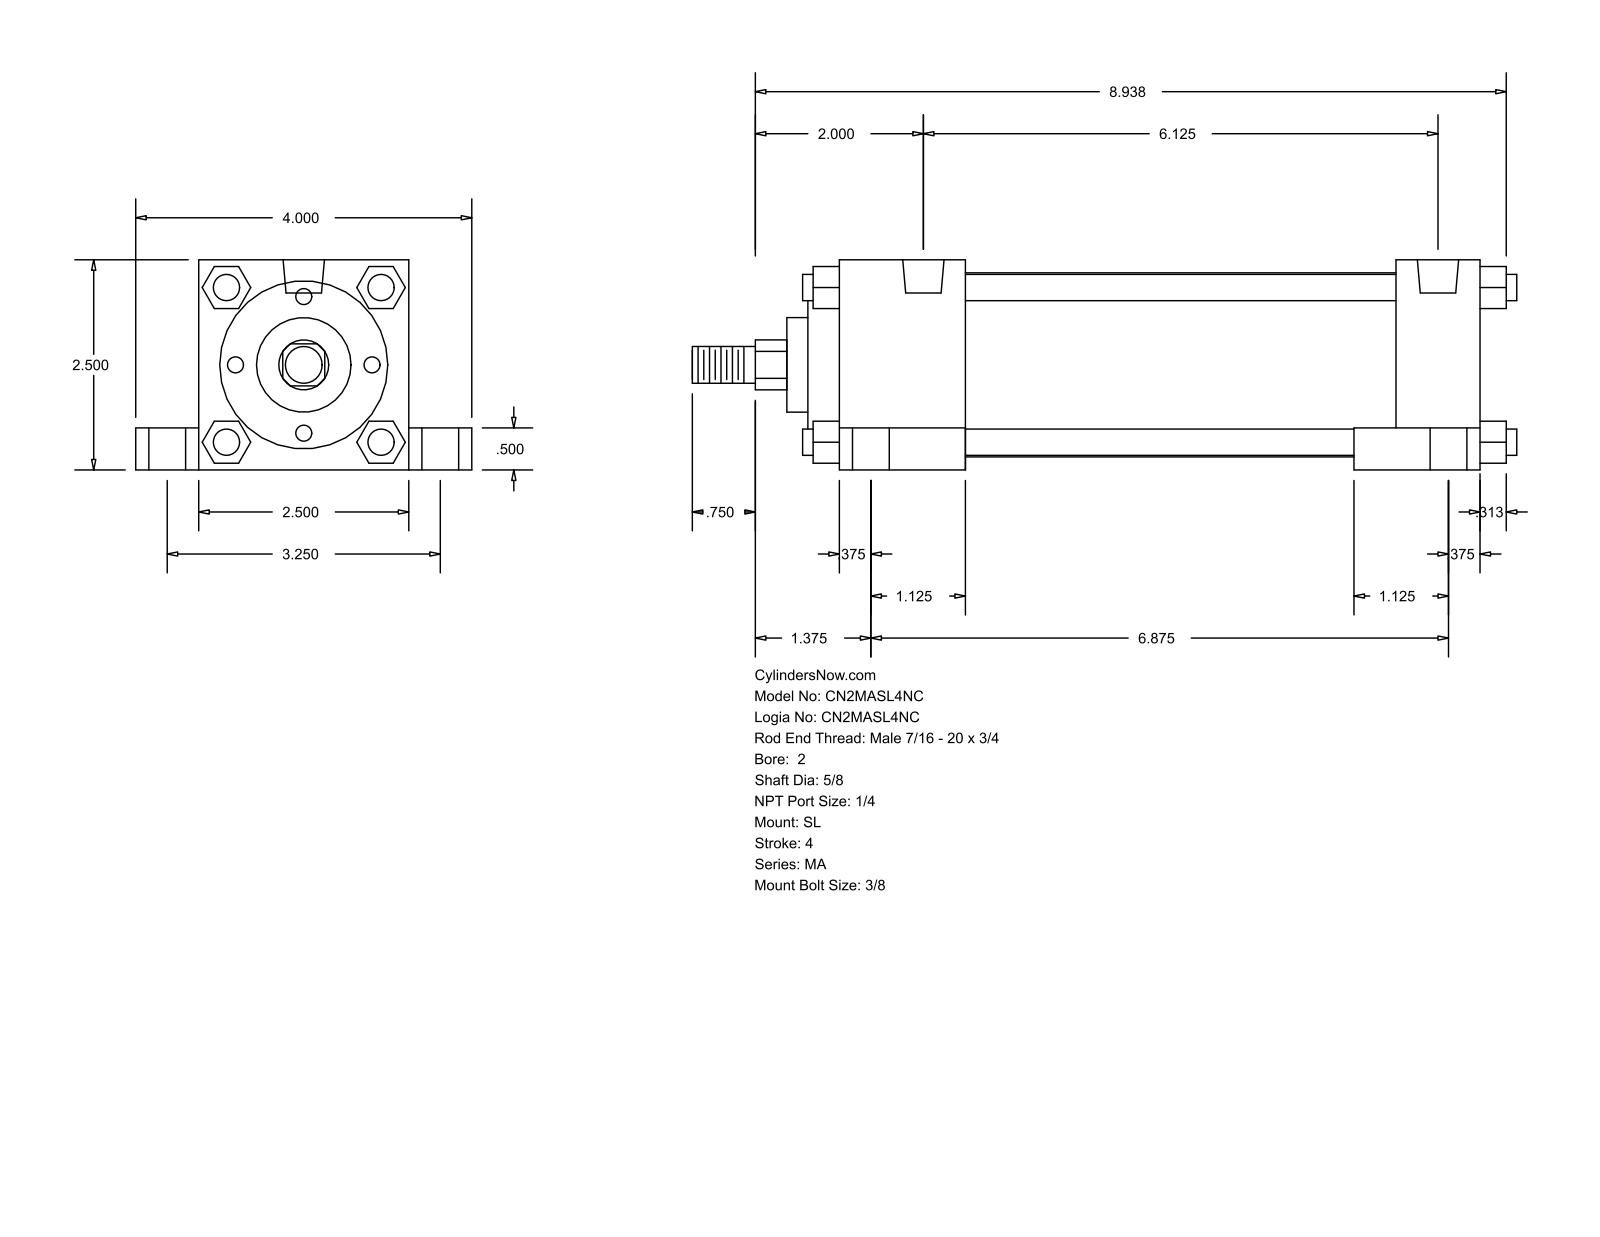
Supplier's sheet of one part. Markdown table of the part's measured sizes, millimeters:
| quantity | value |
| --- | --- |
| part name | MA_SL__0200_0.625 |
| STEP written by | GSSL Pune (CONFIG_CONTROL_DESIGN) |
| units | millimeters |
| bodies | 0 solids, 150 faces (113 planar, 37 cylindrical, 0 other) |
| overall size | 249.24 × 101.6 × 63.5 |
| round holes (diameter × count) | 7.94 × 4, 11.11 × 4, 17.46 × 4, 12.49 × 2 |
| round bosses / shafts (diameter × count) | 7.94 × 4, 55.63 × 1, 50.8 × 1, 28.57 × 1, 15.88 × 1, 11.11 × 1 |
| partial cylindrical surfaces (radius × count) | 7.54 × 1 |
| main face-to-face distances | 63.5, 12.7, 9.52, 19.05, 82.55, 38.1, 50.8, 193.67, 155.57, 168.28 |
| hole center spacings | 41.39, 44.22, 82.54, 155.58, 164.03, 174.63, 176.36, 193.15 |
